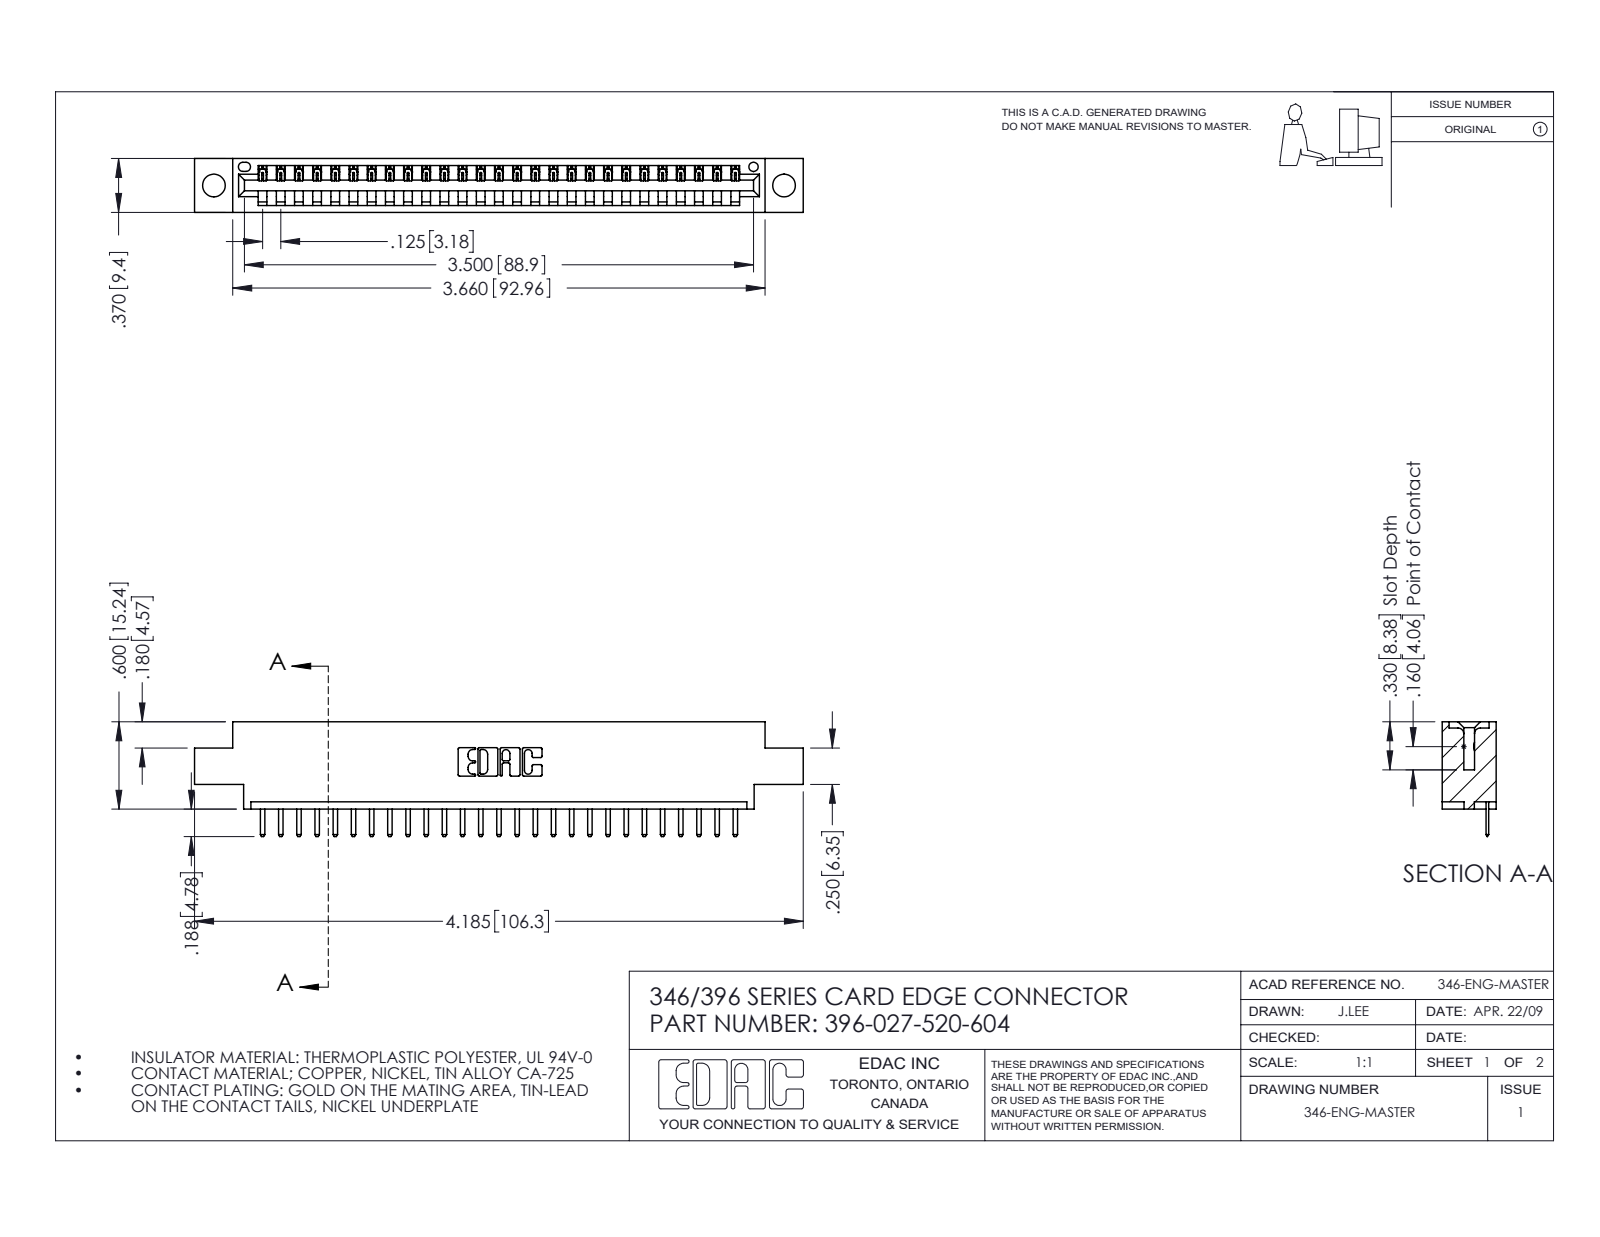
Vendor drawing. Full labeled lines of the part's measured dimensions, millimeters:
Part name (STEP PRODUCT): 345-292-001_345-293-120; 346 Part_0.170 Offset - 0.156 Dia-TH; 396-027-520-604
STEP written by: SolidWorks 2016 (CONFIG_CONTROL_DESIGN)
Units: millimetres
Bodies: 28 solids, 1800 faces (1214 planar, 586 cylindrical, 0 other)
Overall size (bounding box): 106.3 × 20 × 9.4
Volume: 9 750 mm³ · Surface area: 11 740 mm²
Round holes (diameter × count): ⌀4 ×2, ⌀1.6 ×1
Partial cylindrical surfaces — rounded edges, fillets, slot ends (radius × count): R0.3 ×56, R0.2 ×54, R0.3 ×22, R0.2 ×6, R0.8 ×6, R0.7 ×3, R0.8 ×2, R1 ×2
Main face-to-face distances: 1.2, 8.2, 9.4, 6.4, 3.8, 5.6, 2.5, 4.4, 1.8, 7.6
Hole centre spacings: 6.2, 94.3, 99.6
